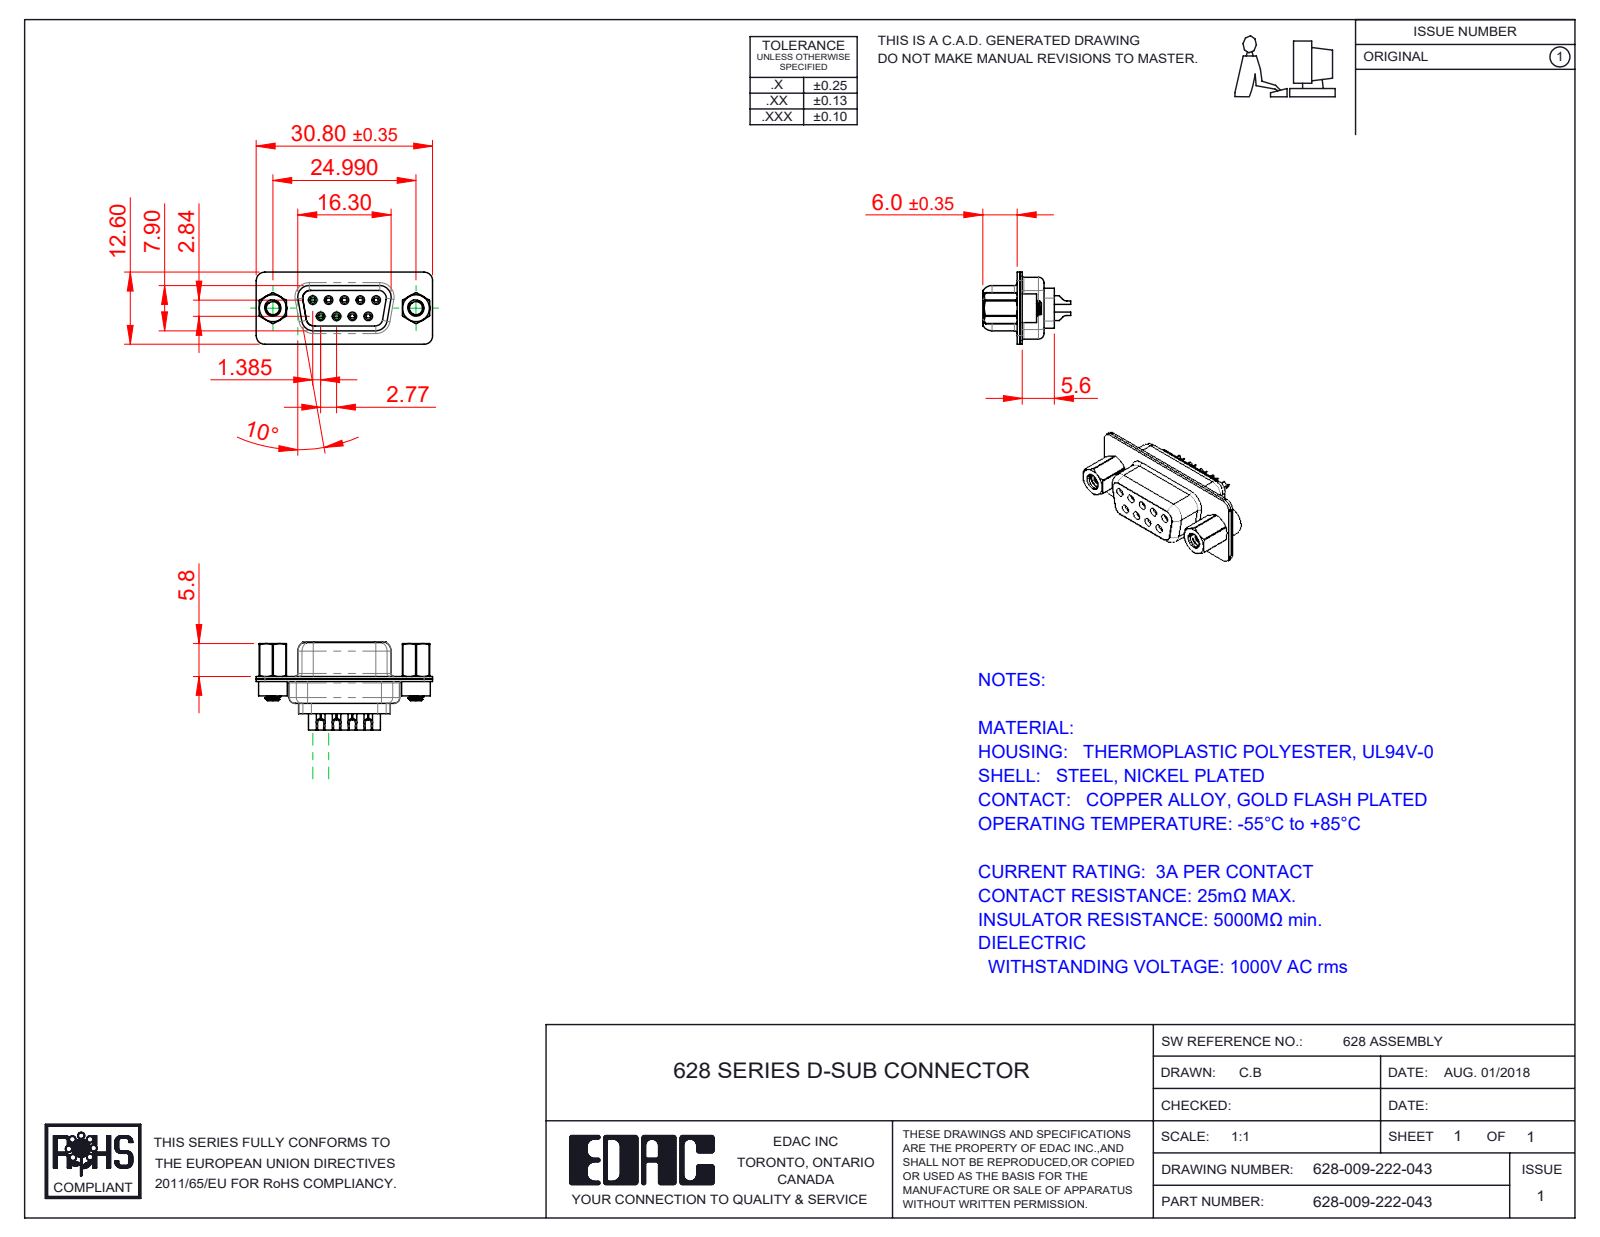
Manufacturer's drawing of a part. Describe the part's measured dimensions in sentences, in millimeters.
The part is named "628 4-40 Hex Standoff; 628 Shell Rear_09 Contacts; 628 Shell Front_09 Contacts; 628 Contact Row 2_22L (+4 more)". Its 3-D file was written by "SolidWorks 2020 (CONFIG_CONTROL_DESIGN)". It is 16 solids with 1202 faces: 278 planar, 432 cylindrical and 492 other. Overall it measures 30.8 by 15.35 by 12.6 millimeters. Its volume is 1 969 cubic millimeters and its surface area 4 997 square millimeters. Round holes: 9 of diameter 0.8, 9 of diameter 0.9, 9 of diameter 1.1, 9 of diameter 1.6, 5 of diameter 1.7, 2 of diameter 2.26, 2 of diameter 2.29, 2 of diameter 4, 2 of diameter 4.05, 2 of diameter 4.85. Round bosses or shafts: 9 of diameter 2, 9 of diameter 1.5, 9 of diameter 1.2, 2 of diameter 5, 2 of diameter 4.95, 2 of diameter 4.8, 2 of diameter 2.79. Partial cylindrical surfaces (rounded edges, fillets, slot ends): 17 of radius 1.5, 12 of radius 2, 9 of radius 0.28, 6 of radius 1, 6 of radius 1.35, 4 of radius 0.25, 4 of radius 0.5, 4 of radius 0.6. The main face-to-face distances are 0.45, 0.4, 0.9, 1.9, 8.5, 6.6, 1.4, 0.5, 12.5, 8.9. The hole center spacings are 3.16, 2.77, 5.54, 5.03, 5.04, 8.31, 7.48, 7.49.
